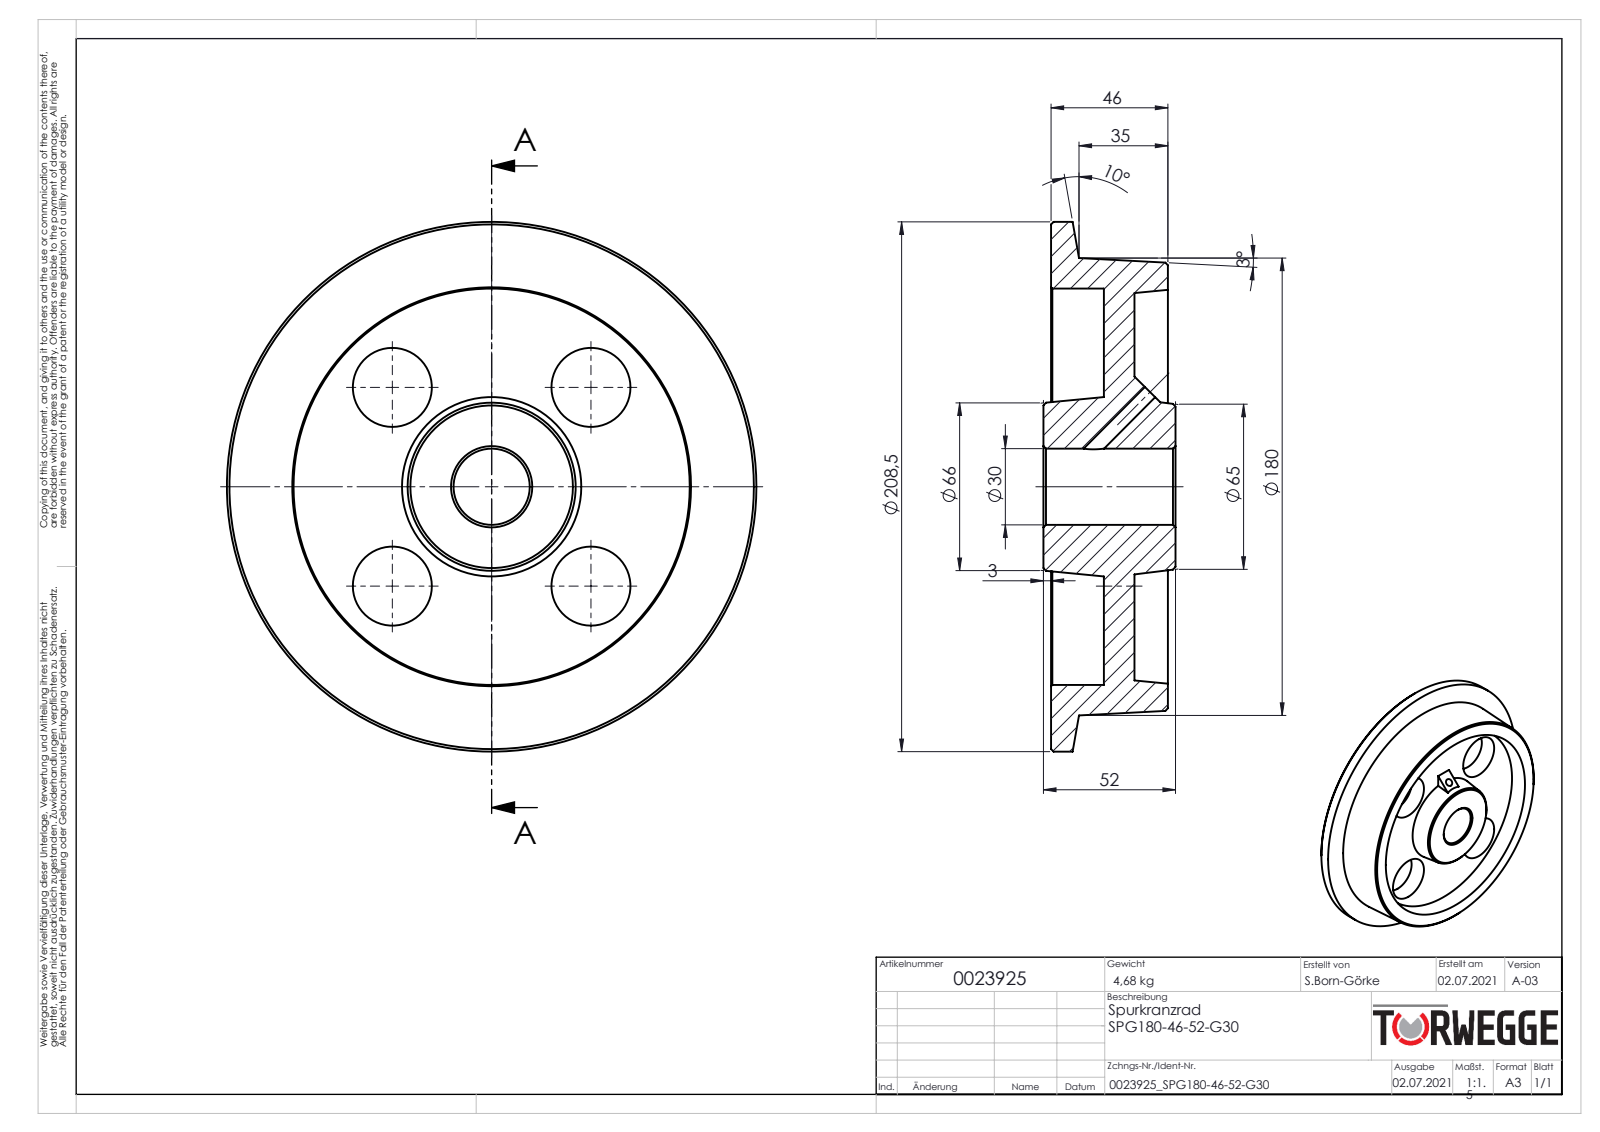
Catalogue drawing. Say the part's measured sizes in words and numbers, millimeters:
The part is named "0023925". Its 3-D file was written by "SolidWorks 2020 (AUTOMOTIVE_DESIGN)". It is 1 solid with 49 faces: 9 planar, 8 cylindrical and 32 other. Overall it measures 208.5 by 208.5 by 52 millimeters. Its volume is 660 677 cubic millimeters and its surface area 117 290 square millimeters. Round holes: 1 of diameter 5.7, 1 of diameter 30, 1 of diameter 156. Round bosses or shafts: 1 of diameter 208.5. The main face-to-face distances are 20.8, 32.84, 12.04, 46, 25.2, 13.16, 3, 49, 23.8, 35.84.
